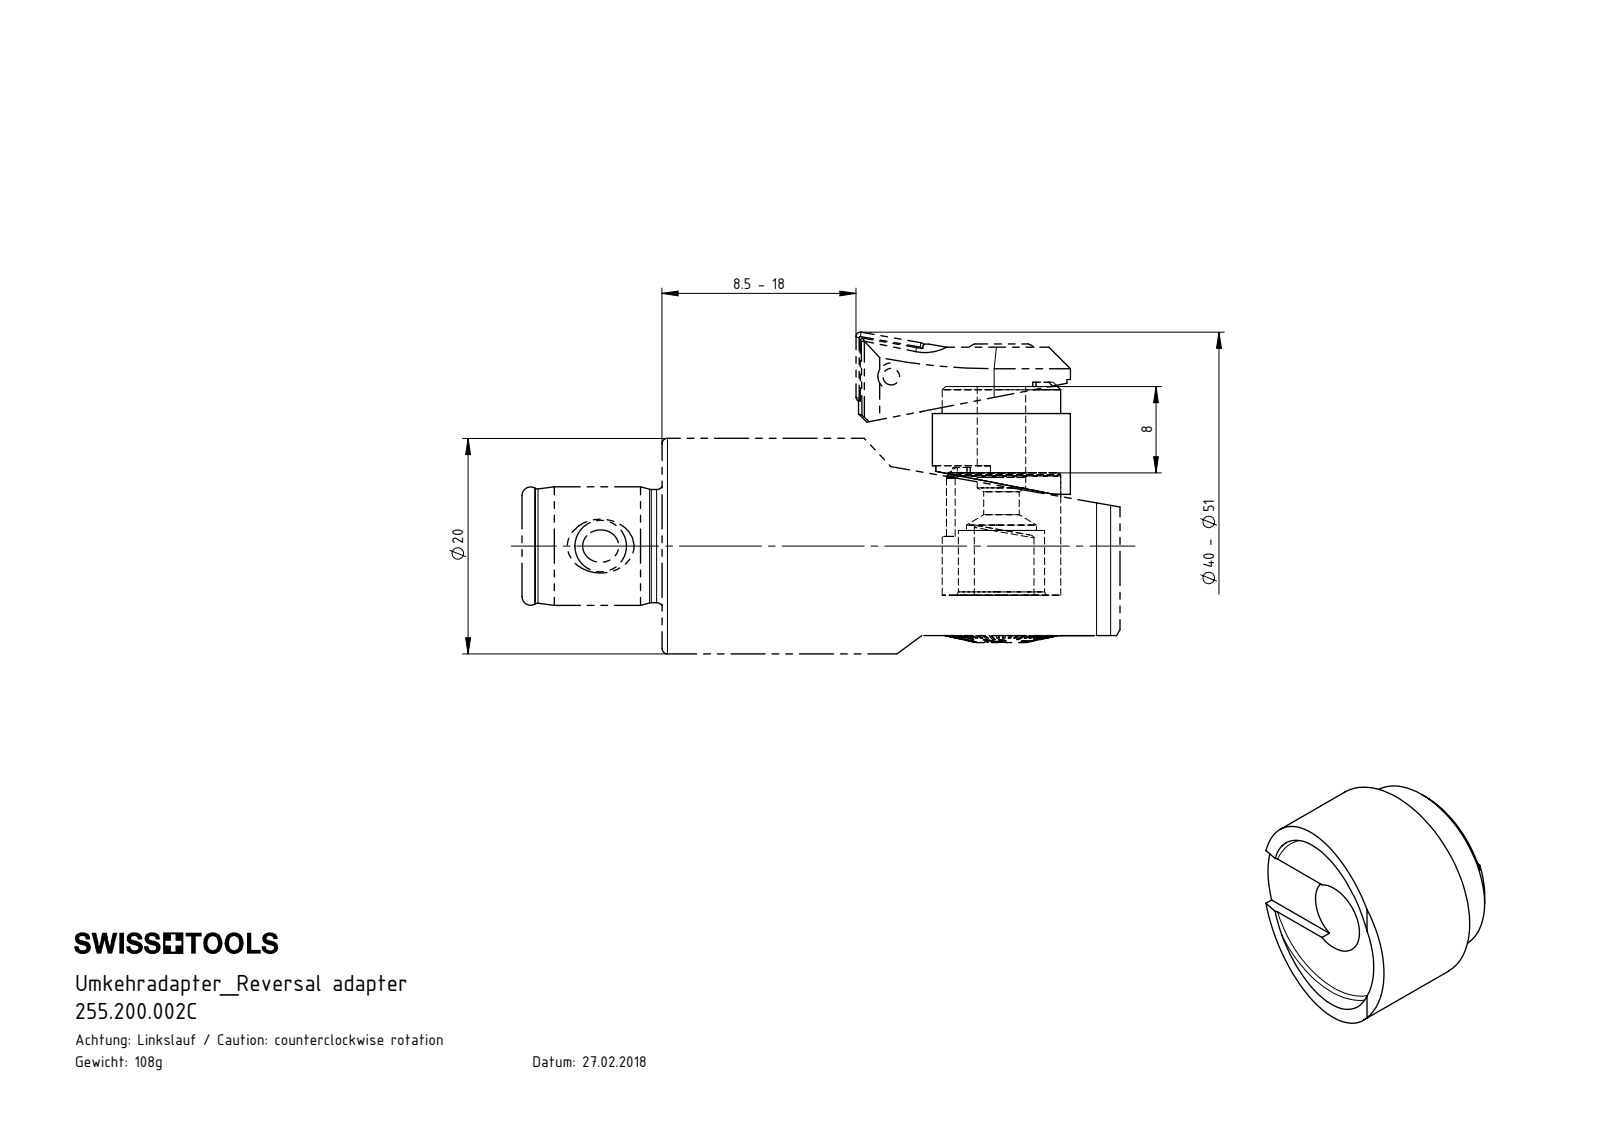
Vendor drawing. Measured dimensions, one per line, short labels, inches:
name: 255.200.002C; F20-U00.001.008_B
written by: SolidWorks 2017 (CONFIG_CONTROL_DESIGN)
unit: in
bodies: 1 solid, 29 faces (13 planar, 11 cylindrical, 5 other)
size: 0.504 × 0.504 × 0.409
volume: 0.051 in³; area: 1.11 in²
holes: 1× ⌀0.177, 1× ⌀0.433
bosses: 1× ⌀0.504
rounds: 2× R0.012
face distances: 0.315, 0.098, 0.217, 0.289, 0.191, 0.026, 0.016, 0.114, 0.305, 0.331
